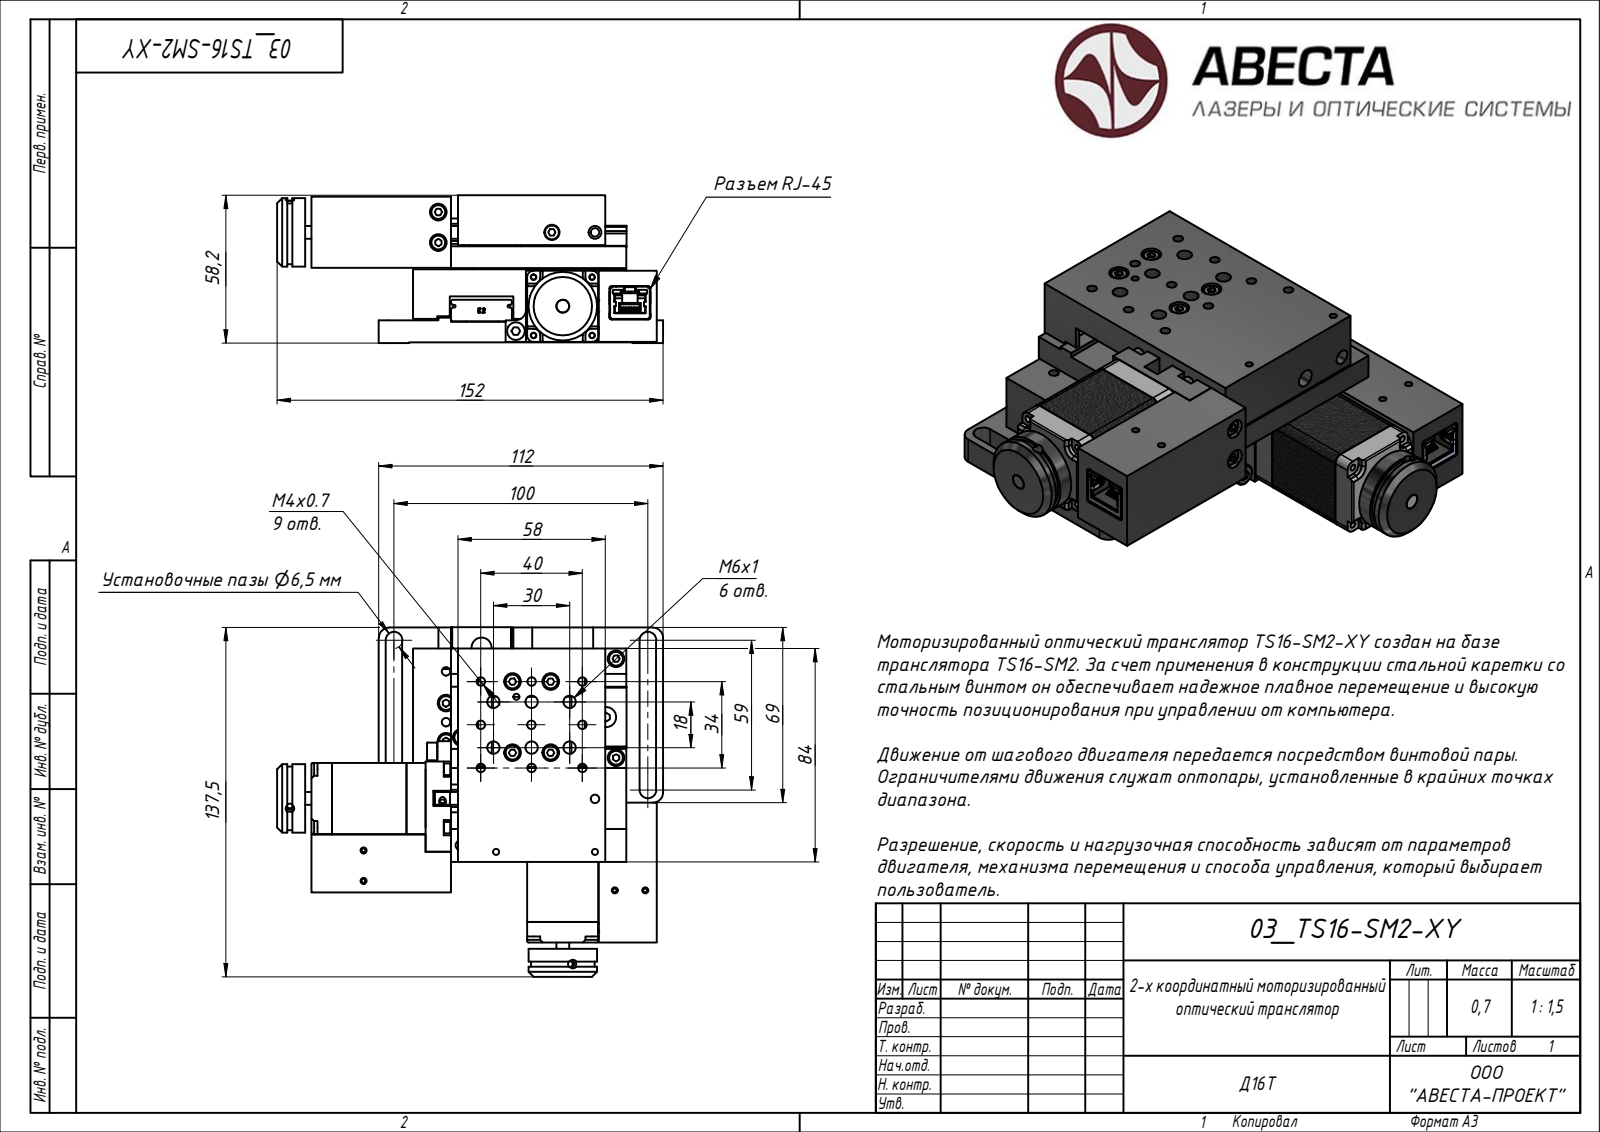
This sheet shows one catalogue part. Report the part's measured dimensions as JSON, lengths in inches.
{"step_written_by": "Rhino 7.34 (AUTOMOTIVE_DESIGN)", "units": "inches", "bodies": {"solids": 217, "faces": 6327, "planar": 4011, "cylindrical": 1686, "other": 630}, "overall_size": [5.984, 5.423, 2.291], "volume_in3": 23.91, "surface_area_in2": 292.7, "round_holes": [[0.128, 30], [0.134, 17], [0.035, 16], [0.097, 15], [0.256, 15], [0.041, 10], [0.194, 9], [0.038, 8], [0.063, 8], [0.081, 8], [0.087, 8], [0.098, 8]], "round_bosses_or_shafts": [[0.118, 23], [0.217, 15], [0.177, 10], [0.098, 10], [0.079, 10], [0.118, 8], [0.026, 8], [0.276, 6]], "partial_cylinders_radius": [[0.005, 48], [0.015, 46], [0.01, 42], [0.007, 38], [0.006, 36], [0.118, 32], [0.039, 26], [0.098, 20]], "face_to_face_distances": [1.146, 0.319, 0.016, 0.807, 0.335, 0.224, 1.13, 1.102, 0.472, 0.661], "hole_center_spacings": [0.669, 0.039, 0.64, 0.906, 0.079, 0.08, 0.406, 0.432]}
